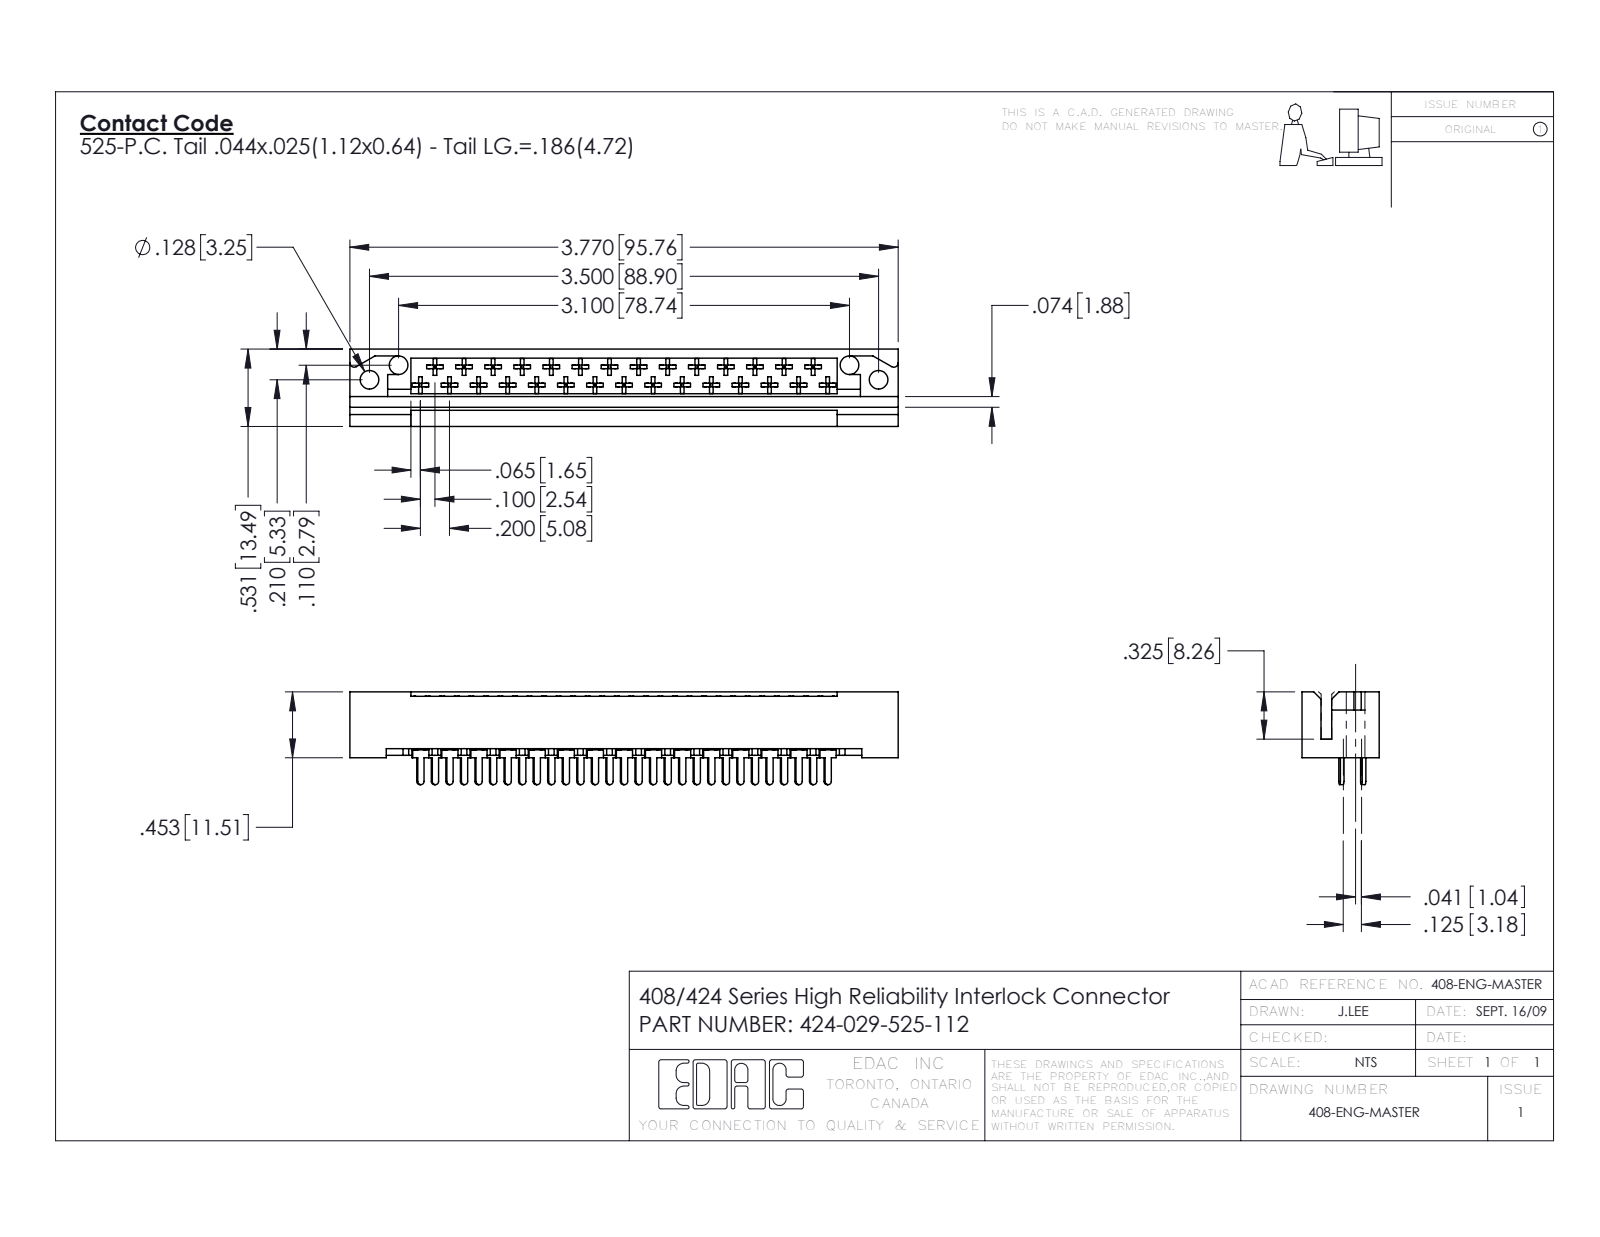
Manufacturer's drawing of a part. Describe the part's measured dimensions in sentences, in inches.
The part is named "408-290-001_408-290-125 - Top; 408-290-001_408-290-125 - Bottom; 424 Part_029; 424-029-525-112". Its 3-D file was written by "SolidWorks 2016 (CONFIG_CONTROL_DESIGN)". It is 30 solids with 1657 faces: 1264 planar, 277 cylindrical and 116 other. Overall it measures 3.77 by 0.638 by 0.531 inches. Its volume is 0.64 cubic inches and its surface area 19.94 square inches. Round holes: 4 of diameter 0.128. Partial cylindrical surfaces (rounded edges, fillets, slot ends): 174 of radius 0.01, 31 of radius 0.02, 29 of radius 0.022, 2 of radius 0.03. The main face-to-face distances are 0.531, 0.025, 0.4, 0.125, 0.1, 0.131, 0.326, 0.259, 0.141, 0.272. The hole center spacings are 0.224, 3.302, 3.1, 3.5.
